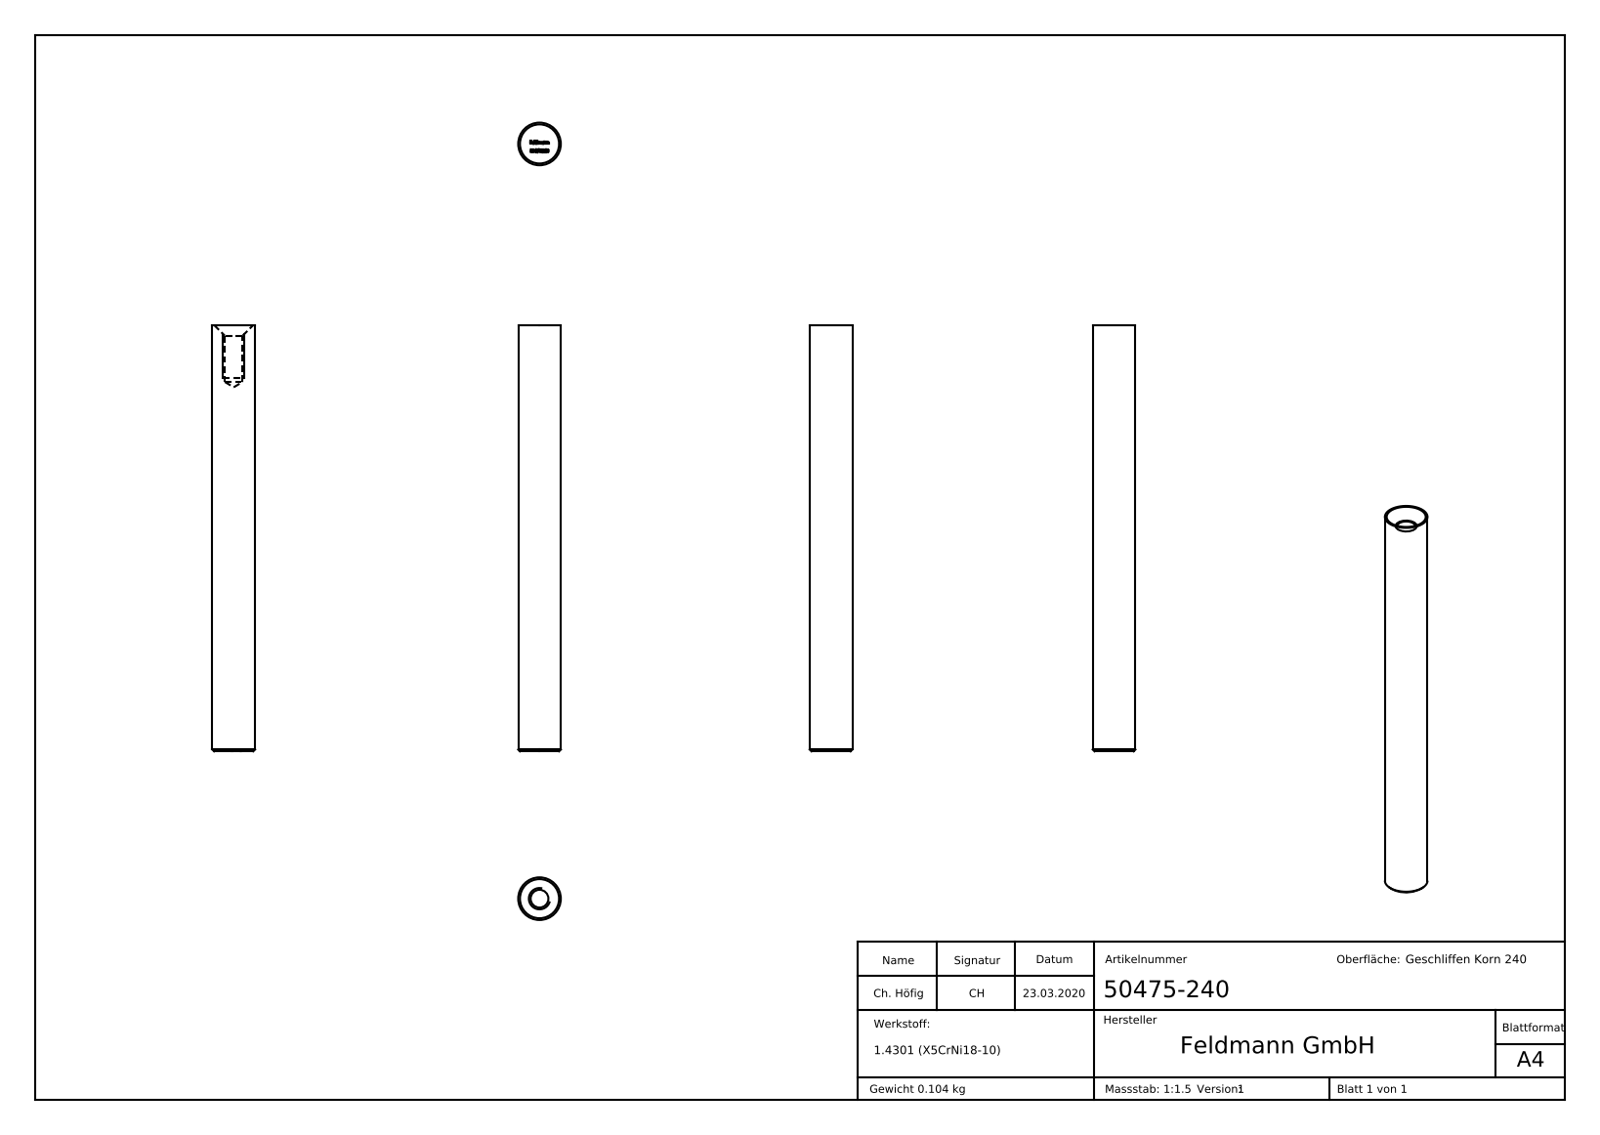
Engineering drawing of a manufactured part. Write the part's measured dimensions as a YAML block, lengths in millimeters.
part_name: "50475-240"
step_written_by: "SolidWorks 2015 (CONFIG_CONTROL_DESIGN)"
units: millimeters
bodies: {solids: 1, faces: 227, planar: 134, cylindrical: 2, other: 91}
overall_size: [120, 12, 12]
volume: 13144
surface_area: 4983
round_holes:
  - {diameter: 5, count: 1}
round_bosses_or_shafts:
  - {diameter: 12, count: 1}
face_to_face_distances: [120, 119.9, 2.41, 1.78, 0.4, 0.53, 0.63, 2.45, 0.83, 0.79]
